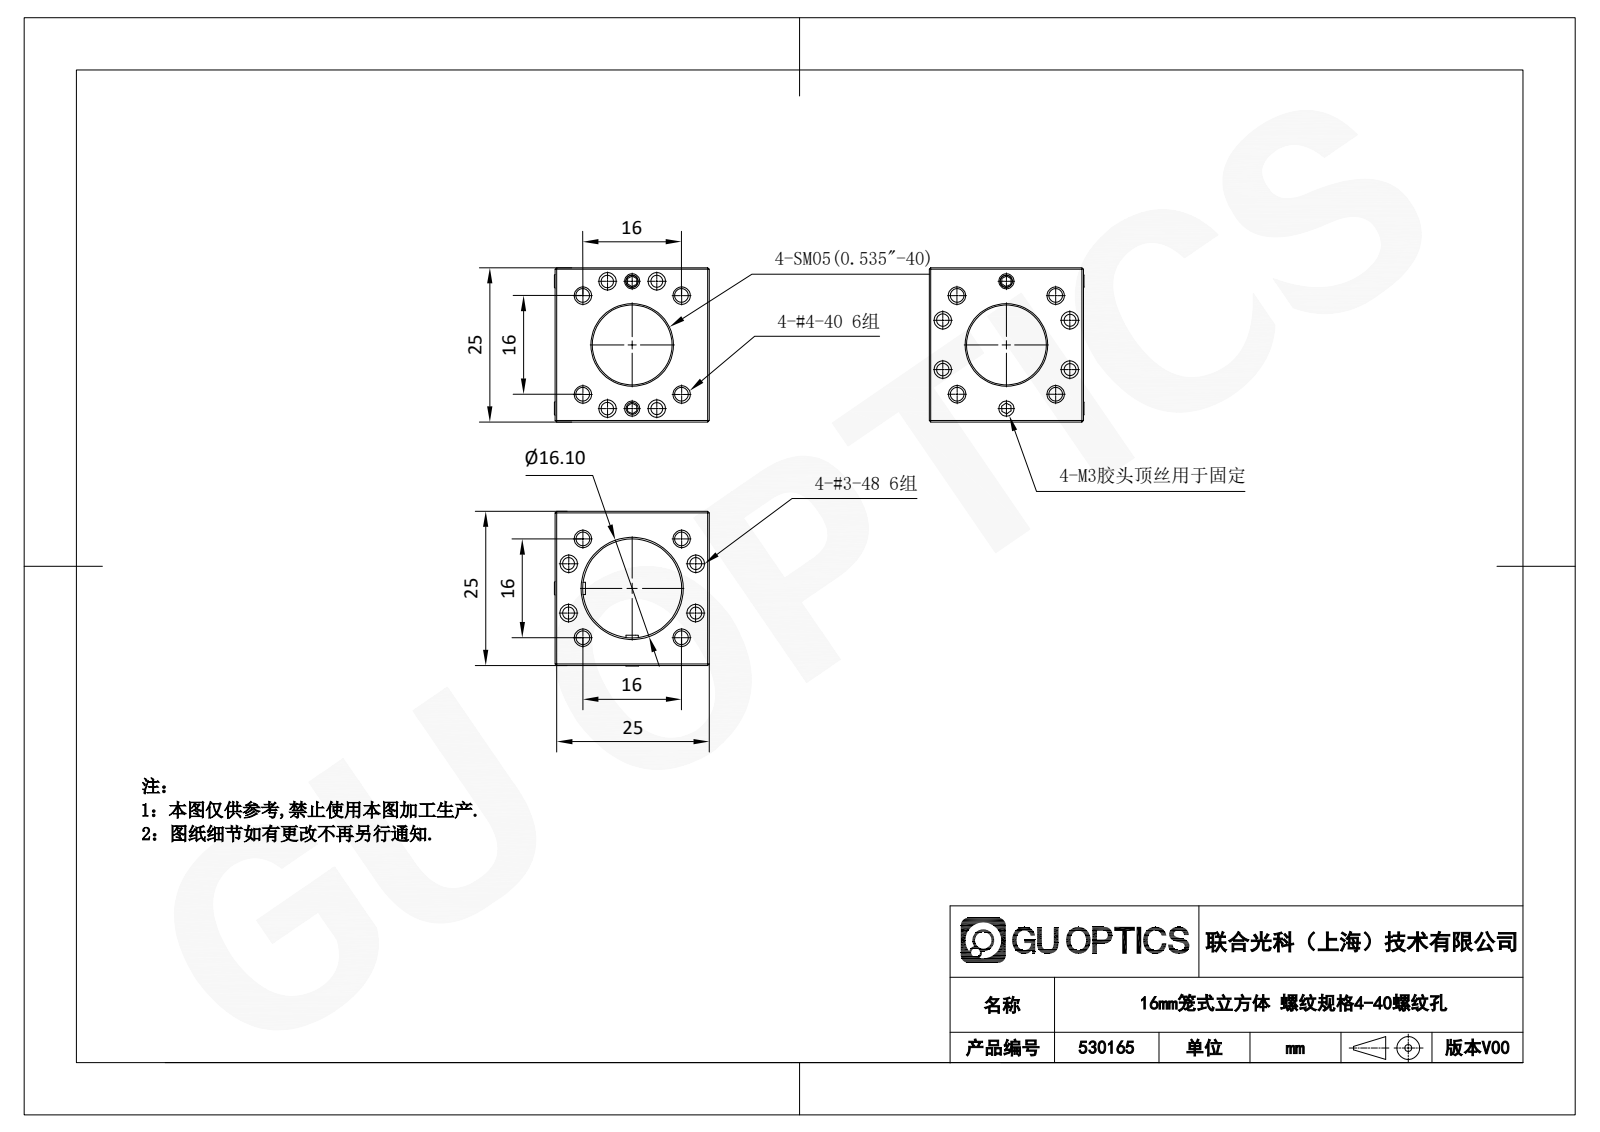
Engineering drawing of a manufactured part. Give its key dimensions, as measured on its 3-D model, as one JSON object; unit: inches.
{"part_name": "530165", "step_written_by": "SolidWorks 2020 (CONFIG_CONTROL_DESIGN)", "units": "inches", "bodies": {"solids": 5, "faces": 338, "planar": 62, "cylindrical": 114, "other": 162}, "overall_size": [0.988, 0.988, 0.984], "volume_in3": 0.43, "surface_area_in2": 9.179, "round_holes": [[0.078, 12], [0.089, 12], [0.098, 4], [0.51, 2], [0.634, 1]], "round_bosses_or_shafts": [[0.118, 4], [0.079, 4]], "face_to_face_distances": [0.984, 1.378, 0.791, 0.193, 0.059, 0.948, 0.157, 0.036, 0.988, 0.197], "hole_center_spacings": [0.181, 0.435, 0.445, 0.481, 0.63, 0.737, 0.861, 0.328]}
